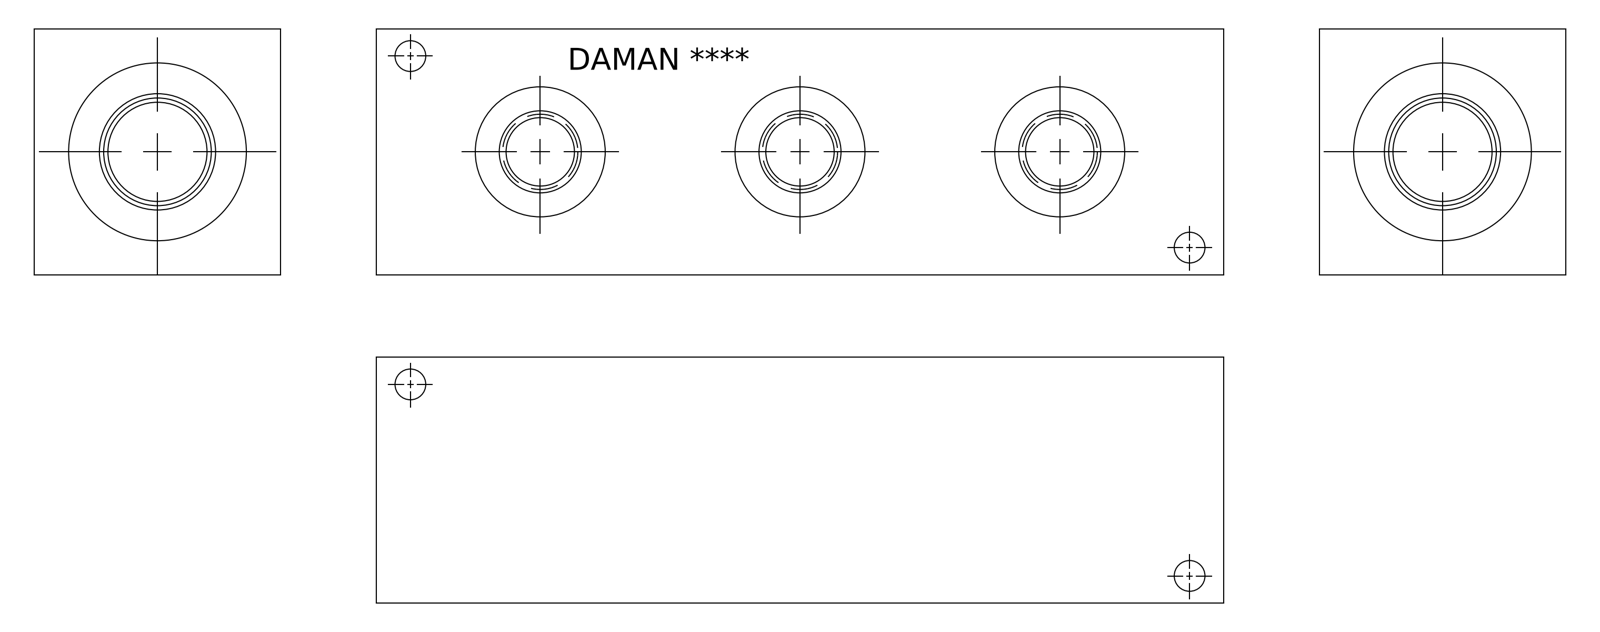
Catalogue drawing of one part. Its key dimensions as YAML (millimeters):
part_name: "Part_AH0000308S_3D"
step_written_by: "Autodesk Inventor 2019 (AUTOMOTIVE_DESIGN)"
units: millimeters
bodies: {solids: 1, faces: 383, planar: 212, cylindrical: 31, other: 140}
overall_size: [196.85, 57.15, 57.15]
volume: 579828
surface_area: 64808
round_holes:
  - {diameter: 7.14, count: 4}
  - {diameter: 17.5, count: 3}
  - {diameter: 19.05, count: 3}
  - {diameter: 19.25, count: 3}
  - {diameter: 30.63, count: 3}
  - {diameter: 15.88, count: 1}
  - {diameter: 23.01, count: 1}
  - {diameter: 24.92, count: 1}
  - {diameter: 26.99, count: 1}
  - {diameter: 27, count: 1}
  - {diameter: 27.43, count: 1}
  - {diameter: 42.04, count: 1}
face_to_face_distances: [57.15, 0.79, 196.85, 196.06, 56.36, 195.27, 19.84, 177.01, 19.05, 176.22]
hole_center_spacings: [37.48, 152.46, 186.39, 60.32, 60.33, 93.19, 93.2, 120.65]
